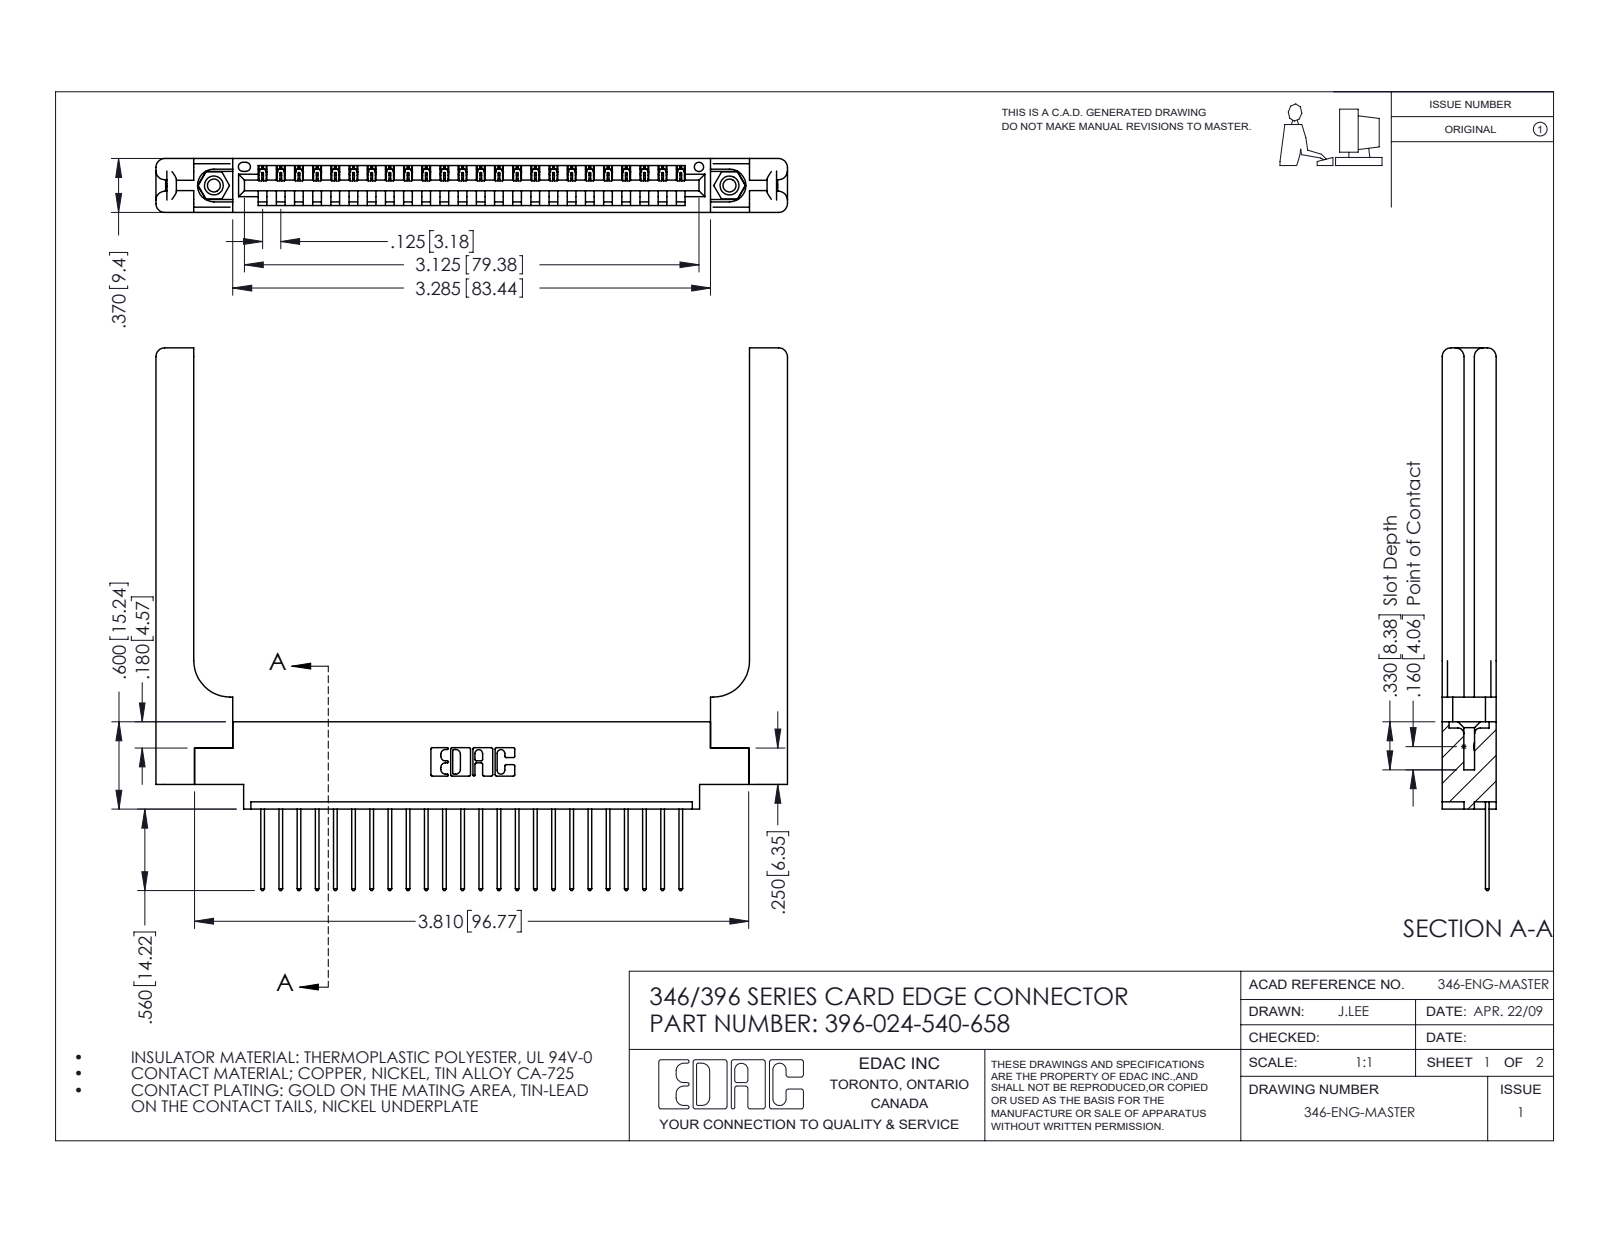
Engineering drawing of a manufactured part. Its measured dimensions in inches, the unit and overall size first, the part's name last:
Units: inches
Overall size (bounding box): 4.341 × 3.73 × 0.37
Round holes (diameter × count): ⌀0.089 ×2, ⌀0.125 ×2, ⌀0.156 ×2, ⌀0.064 ×1
Round bosses / shafts (diameter × count): ⌀0.155 ×2
Partial cylindrical surfaces — rounded edges, fillets, slot ends (radius × count): R0.006 ×48, R0.01 ×48, R0.01 ×22, R0.06 ×16, R0.007 ×6, R0.031 ×6, R0.026 ×3, R0.03 ×2
Main face-to-face distances: 0.37, 0.072, 0.048, 0.322, 0.15, 0.148, 0.25, 0.298, 0.025, 0.102
Hole centre spacings: 0.246, 3.337, 3.545
Volume: 1.088 in³ · Surface area: 28.3 in²
Bodies: 29 solids, 1774 faces (1188 planar, 526 cylindrical, 60 other)
Part name (STEP PRODUCT): 345-292-001_345-293-140; 346 Part_0.170 Offset - 0.156 Dia-TH; 396-024-540-658; 346-220-058_345-220-058 (+1 more)
STEP written by: SolidWorks 2016 (CONFIG_CONTROL_DESIGN)
